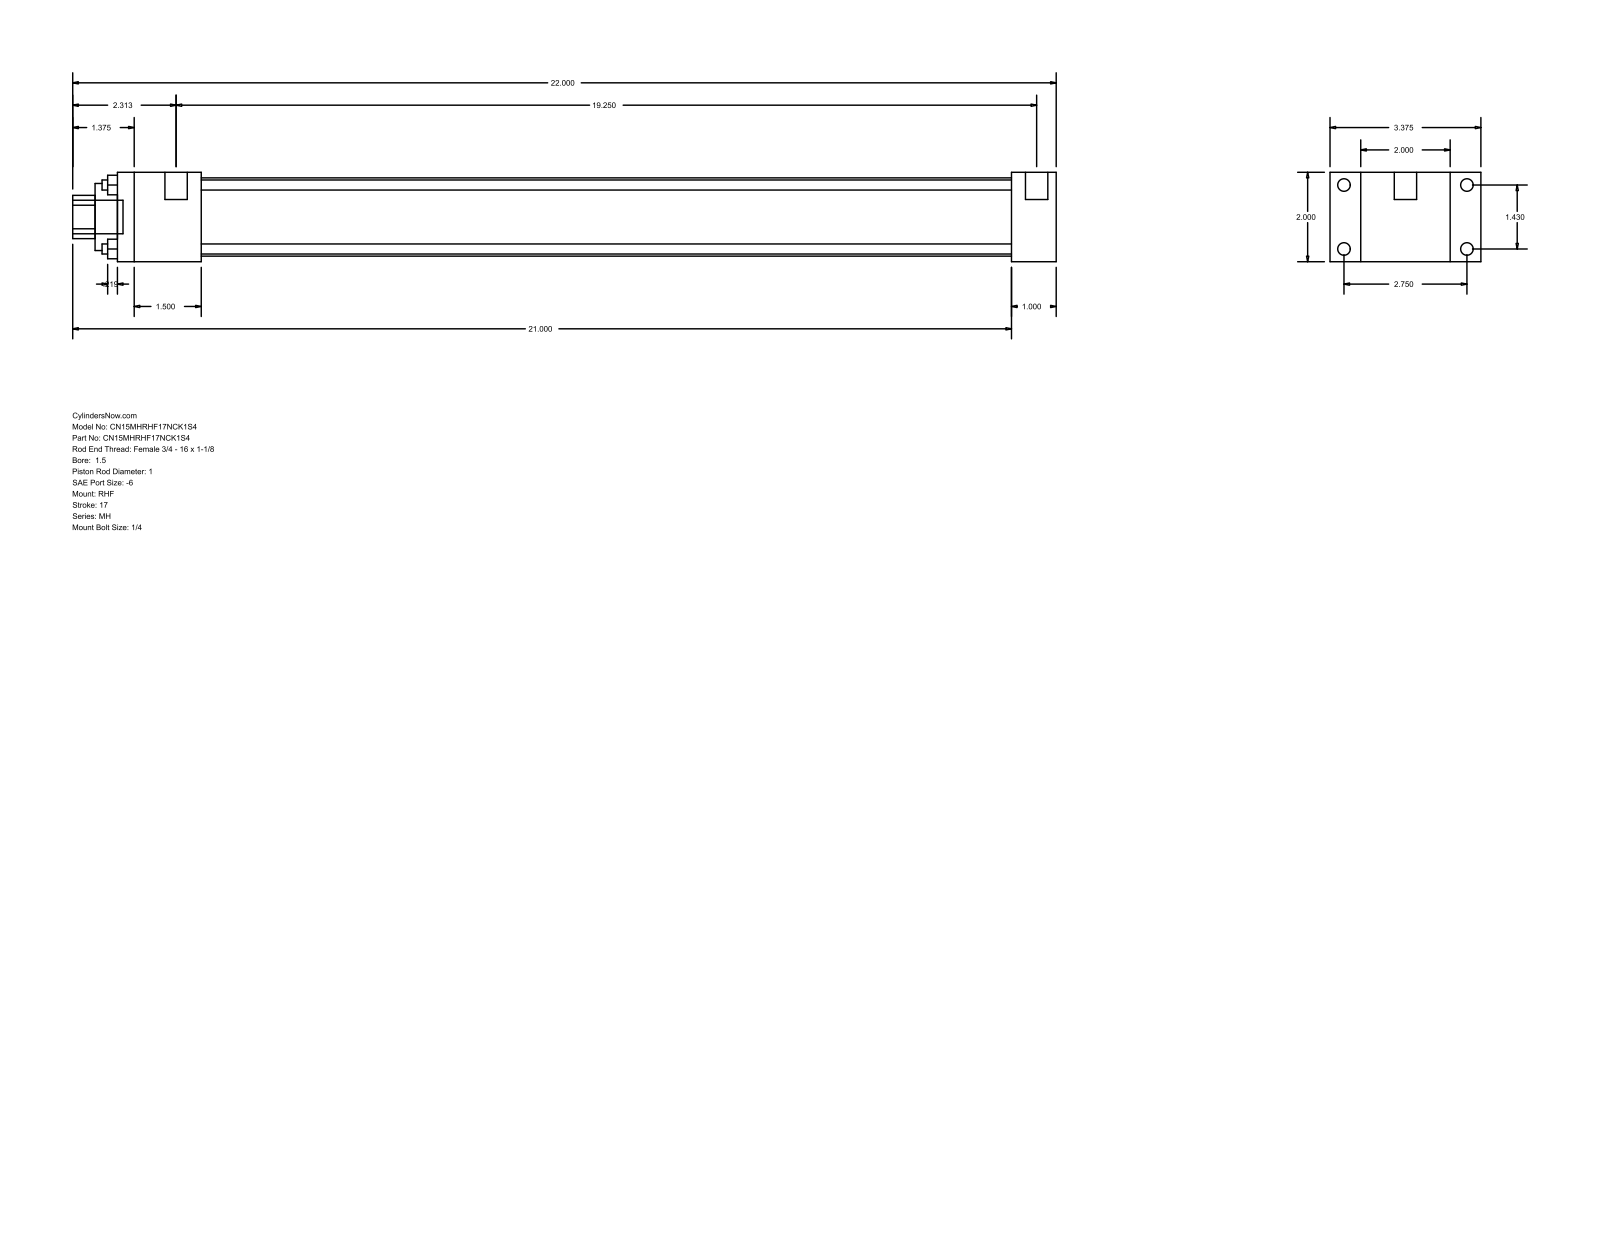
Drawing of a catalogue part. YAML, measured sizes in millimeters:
part_name: "MH_RHF__0150_1"
step_written_by: "GSSL Pune (CONFIG_CONTROL_DESIGN)"
units: millimeters
bodies: {solids: 0, faces: 88, planar: 60, cylindrical: 28, other: 0}
overall_size: [558.8, 85.72, 50.8]
round_holes:
  - {diameter: 5.71, count: 4}
  - {diameter: 25.4, count: 1}
  - {diameter: 38.1, count: 1}
  - {diameter: 44.45, count: 1}
round_bosses_or_shafts:
  - {diameter: 7.14, count: 4}
  - {diameter: 5.56, count: 4}
  - {diameter: 12.7, count: 2}
  - {diameter: 19.05, count: 1}
partial_cylinders:
  - {radius: 12.29, count: 1}
face_to_face_distances: [50.8, 25.4, 17.46, 68.26, 85.72, 533.4, 508, 47.63, 460.37, 485.77]
hole_center_spacings: [25.68, 36.32, 51.36]
